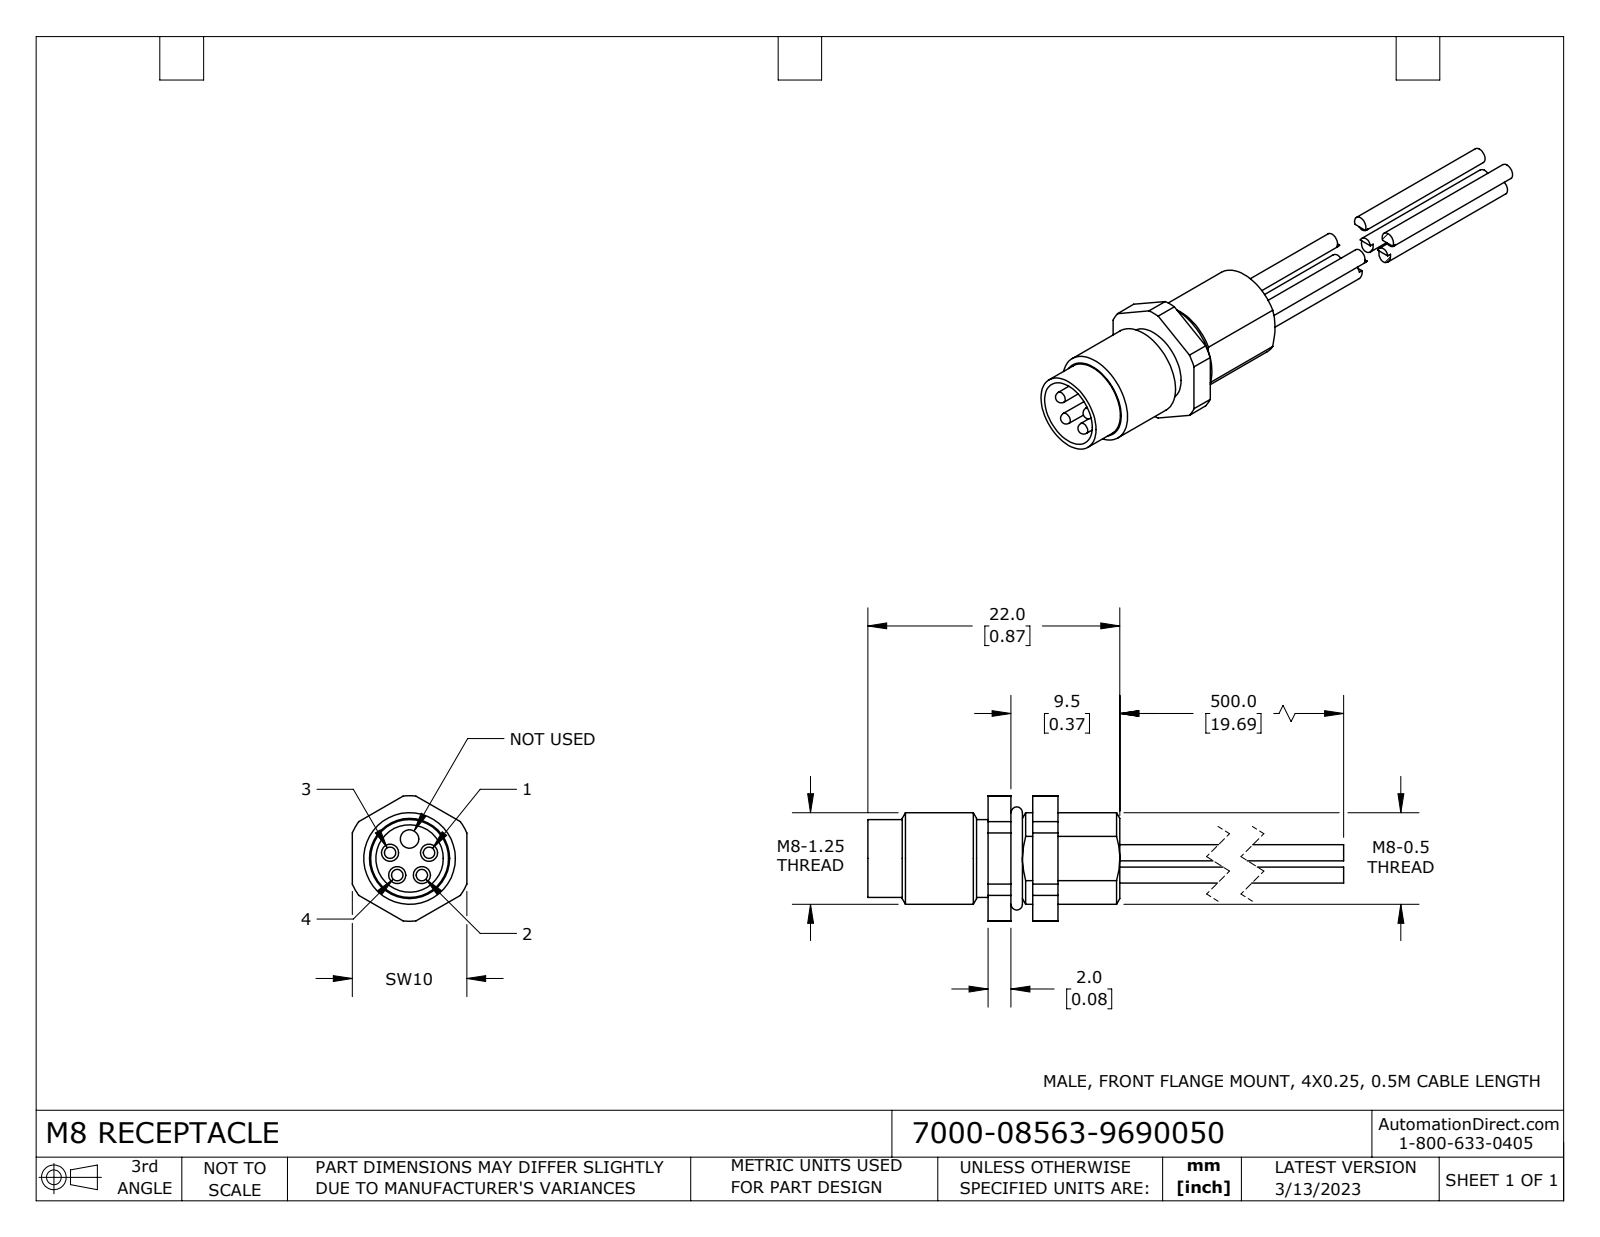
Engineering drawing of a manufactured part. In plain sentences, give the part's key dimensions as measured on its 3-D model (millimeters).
The part is named "7000-08563-9690050". Its 3-D file was written by "SolidWorks 2021 (CONFIG_CONTROL_DESIGN)". It is 7 solids with 112 faces: 38 planar, 54 cylindrical and 20 other. Overall it measures 120 by 10.9 by 10 millimeters. Its volume is 1 600 cubic millimeters and its surface area 3 030 square millimeters. Round holes: 4 of diameter 1.5, 1 of diameter 1.6, 1 of diameter 5.9, 1 of diameter 6.2. Round bosses or shafts: 4 of diameter 1.4, 4 of diameter 1, 1 of diameter 8, 1 of diameter 6.8. Partial cylindrical surfaces (rounded edges, fillets, slot ends): 1 of radius 5.5. The main face-to-face distances are 10, 2, 7.5, 9.5, 8.5, 7, 1.5, 3.4, 5.6, 2.2. The hole center spacings are 1.8, 1.8, 2.1, 2.1, 3.3, 3.4, 1.7, 2.1.
